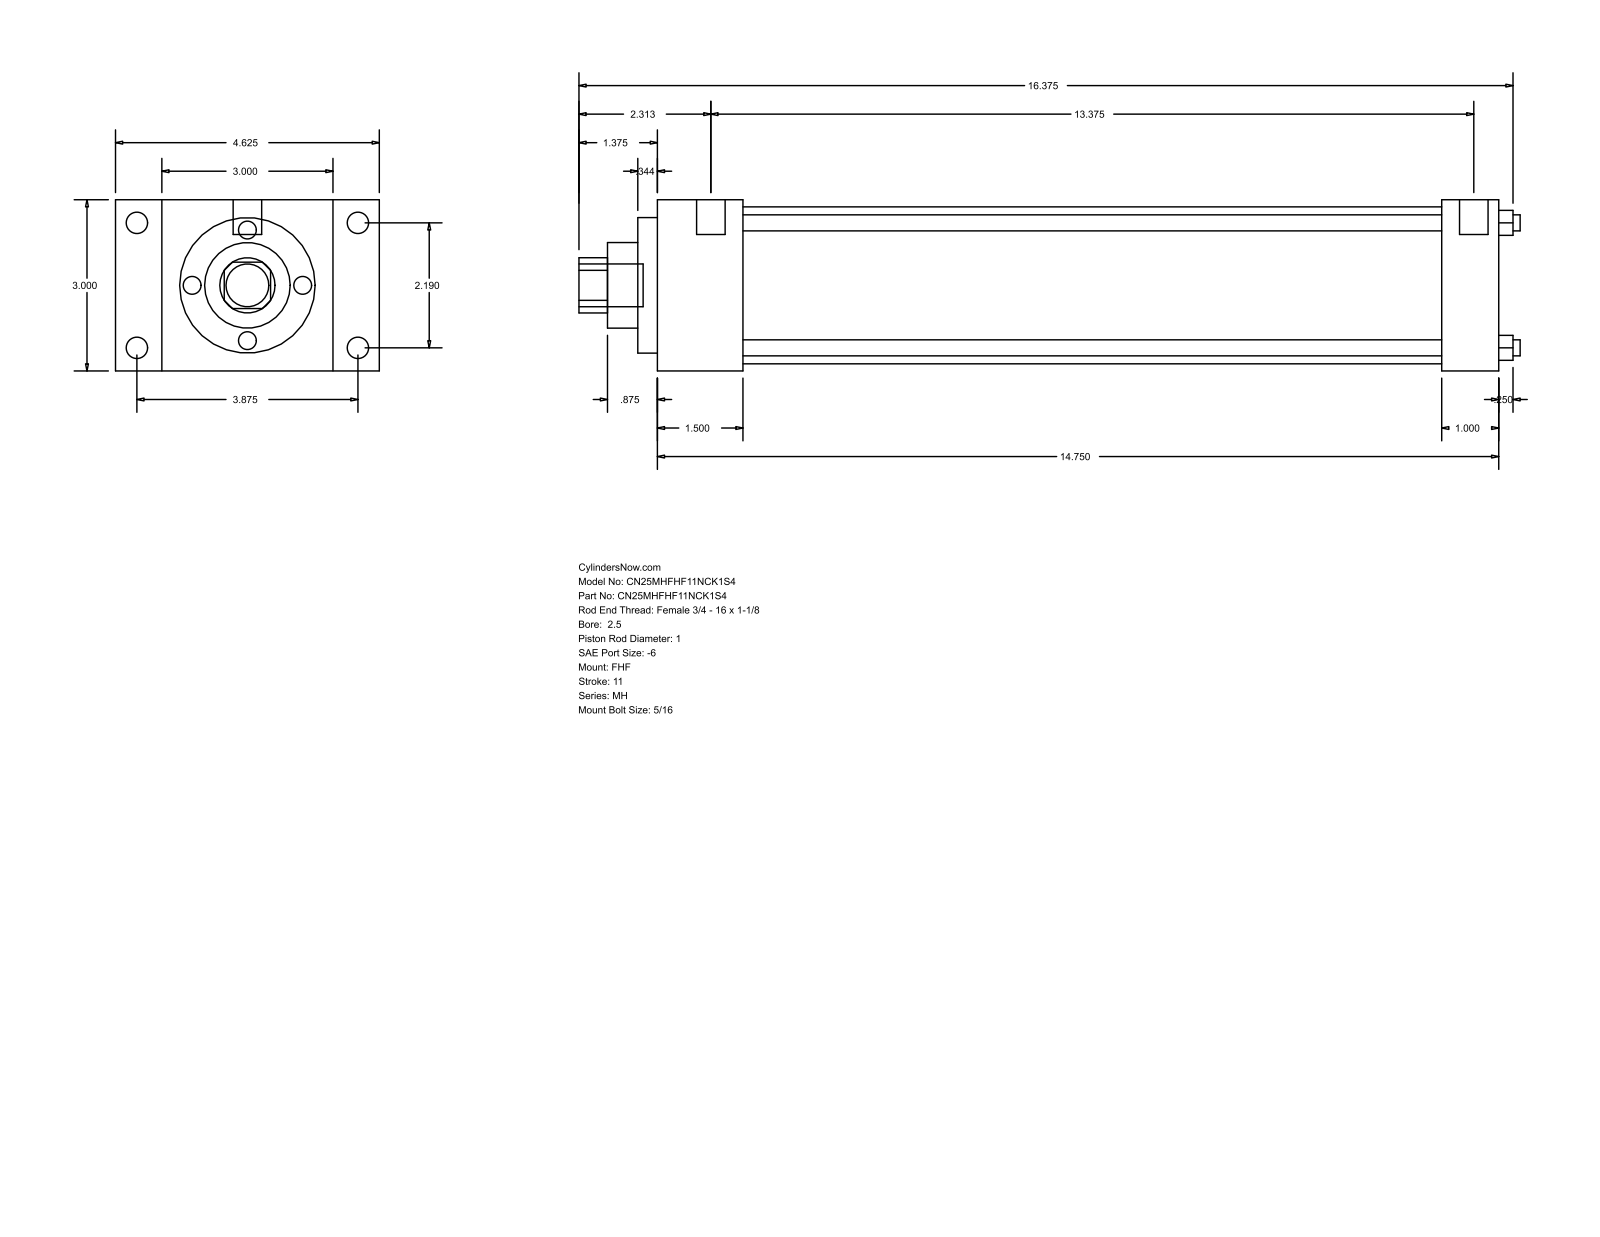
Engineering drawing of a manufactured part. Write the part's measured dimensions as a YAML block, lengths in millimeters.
part_name: "MH_FHF__0250_1"
step_written_by: "GSSL Pune (CONFIG_CONTROL_DESIGN)"
units: millimeters
bodies: {solids: 0, faces: 90, planar: 61, cylindrical: 29, other: 0}
overall_size: [419.1, 117.47, 76.2]
round_holes:
  - {diameter: 7.14, count: 4}
  - {diameter: 25.4, count: 1}
  - {diameter: 38.1, count: 1}
  - {diameter: 60.33, count: 1}
  - {diameter: 69.85, count: 1}
round_bosses_or_shafts:
  - {diameter: 9.53, count: 4}
  - {diameter: 5.56, count: 4}
  - {diameter: 12.7, count: 2}
  - {diameter: 19.05, count: 1}
partial_cylinders:
  - {radius: 12.29, count: 1}
face_to_face_distances: [76.2, 374.65, 38.11, 336.54, 20.64, 96.84, 117.48, 25.39, 349.26, 311.15]
hole_center_spacings: [39.33, 55.62, 78.66]
